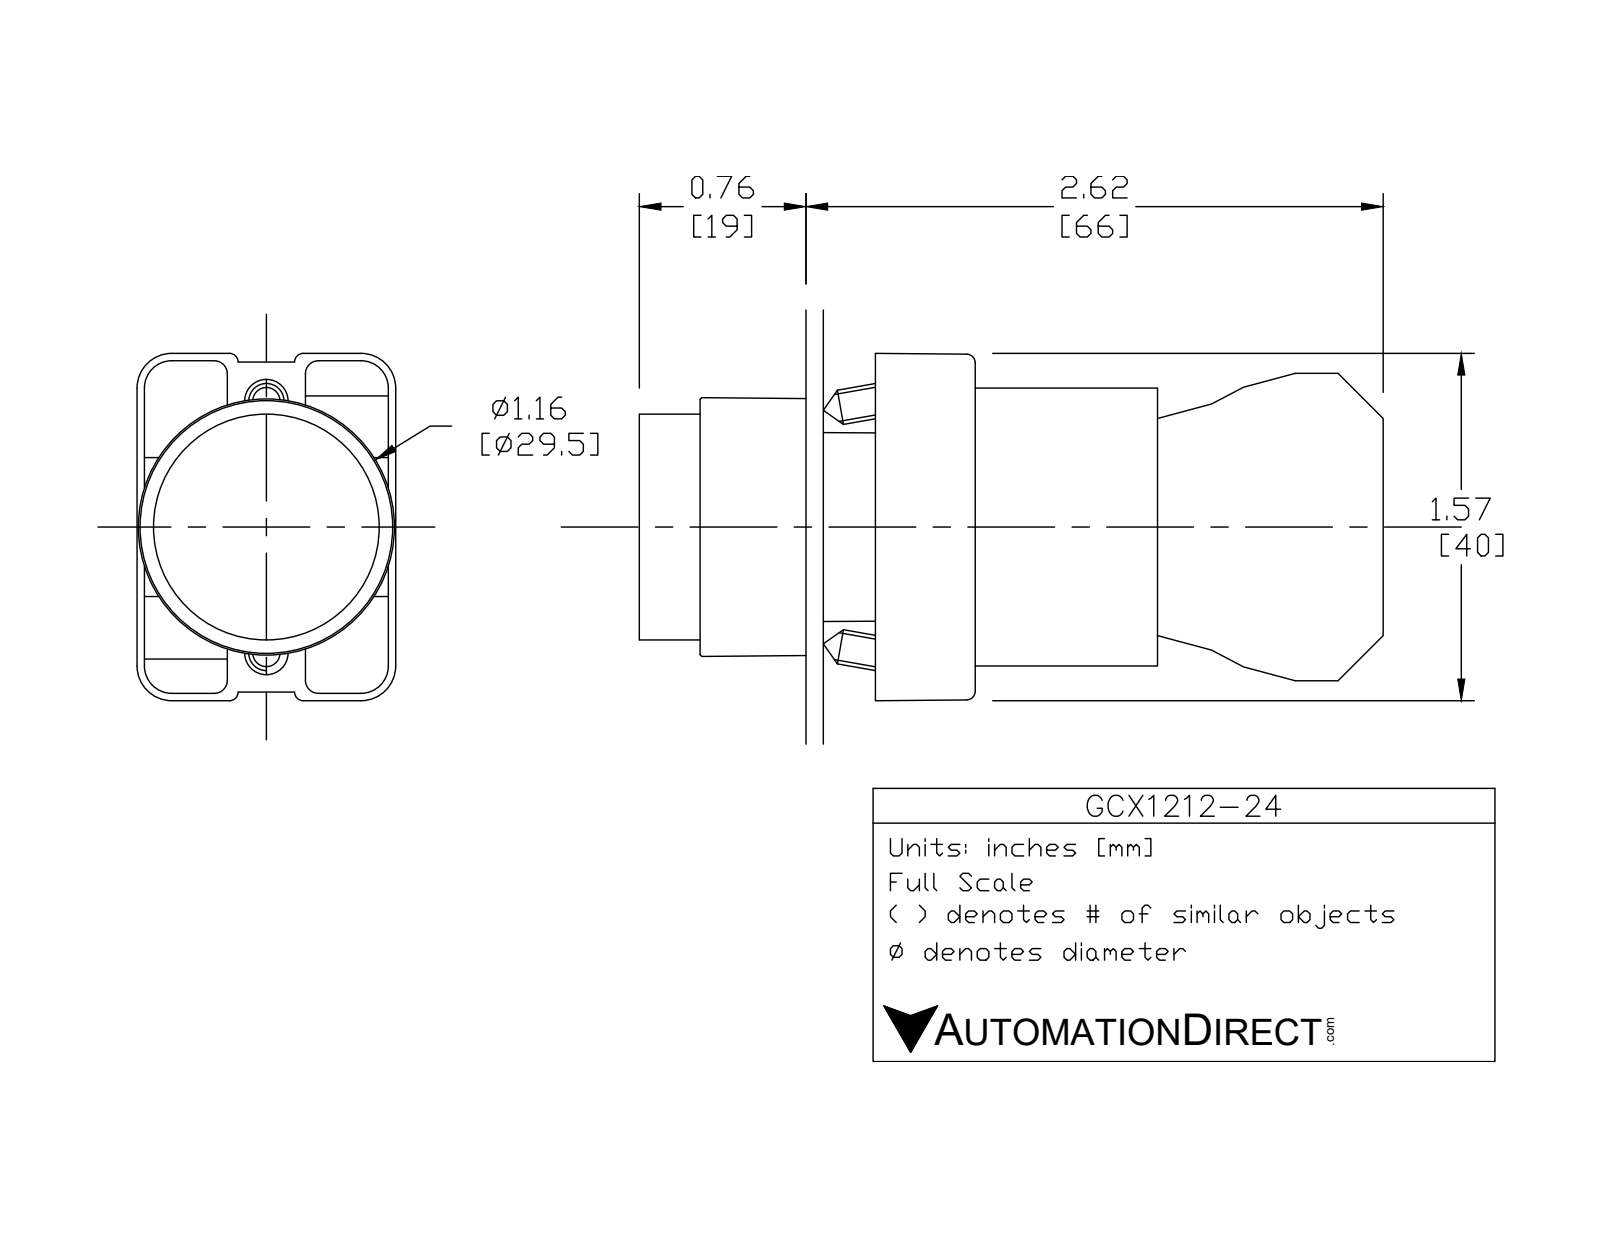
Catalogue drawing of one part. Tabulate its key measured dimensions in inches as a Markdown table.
| quantity | value |
| --- | --- |
| part name | GCX1212 OPERATOR; ECX1050; ecx1040; ecx1029 (+1 more) |
| STEP written by | SolidWorks 2016 (AUTOMOTIVE_DESIGN) |
| units | inches |
| bodies | 7 solids, 425 faces (250 planar, 144 cylindrical, 31 other) |
| overall size | 3.319 × 1.581 × 1.177 |
| volume | 2.721 in³ |
| surface area | 36.32 in² |
| round holes (diameter × count) | 0.079 × 2, 0.124 × 2, 0.13 × 2, 0.087 × 1, 0.197 × 1, 0.469 × 1, 0.878 × 1, 0.888 × 1, 1.024 × 1 |
| round bosses / shafts (diameter × count) | 0.157 × 4, 1.175 × 1, 1.004 × 1, 0.945 × 1, 0.856 × 1, 0.78 × 1, 0.504 × 1 |
| partial cylindrical surfaces (radius × count) | 0.059 × 24, 0.041 × 12, 0.124 × 12, 0.157 × 12, 0.039 × 8, 0.128 × 2, 0.02 × 1, 0.063 × 1 |
| main face-to-face distances | 0.827, 0.579, 1.171, 2.02, 1.193, 0.031, 0.033, 0.573, 1.165, 0.593 |
| hole center spacings | 0.236, 0.544, 0.472, 0.49 |
